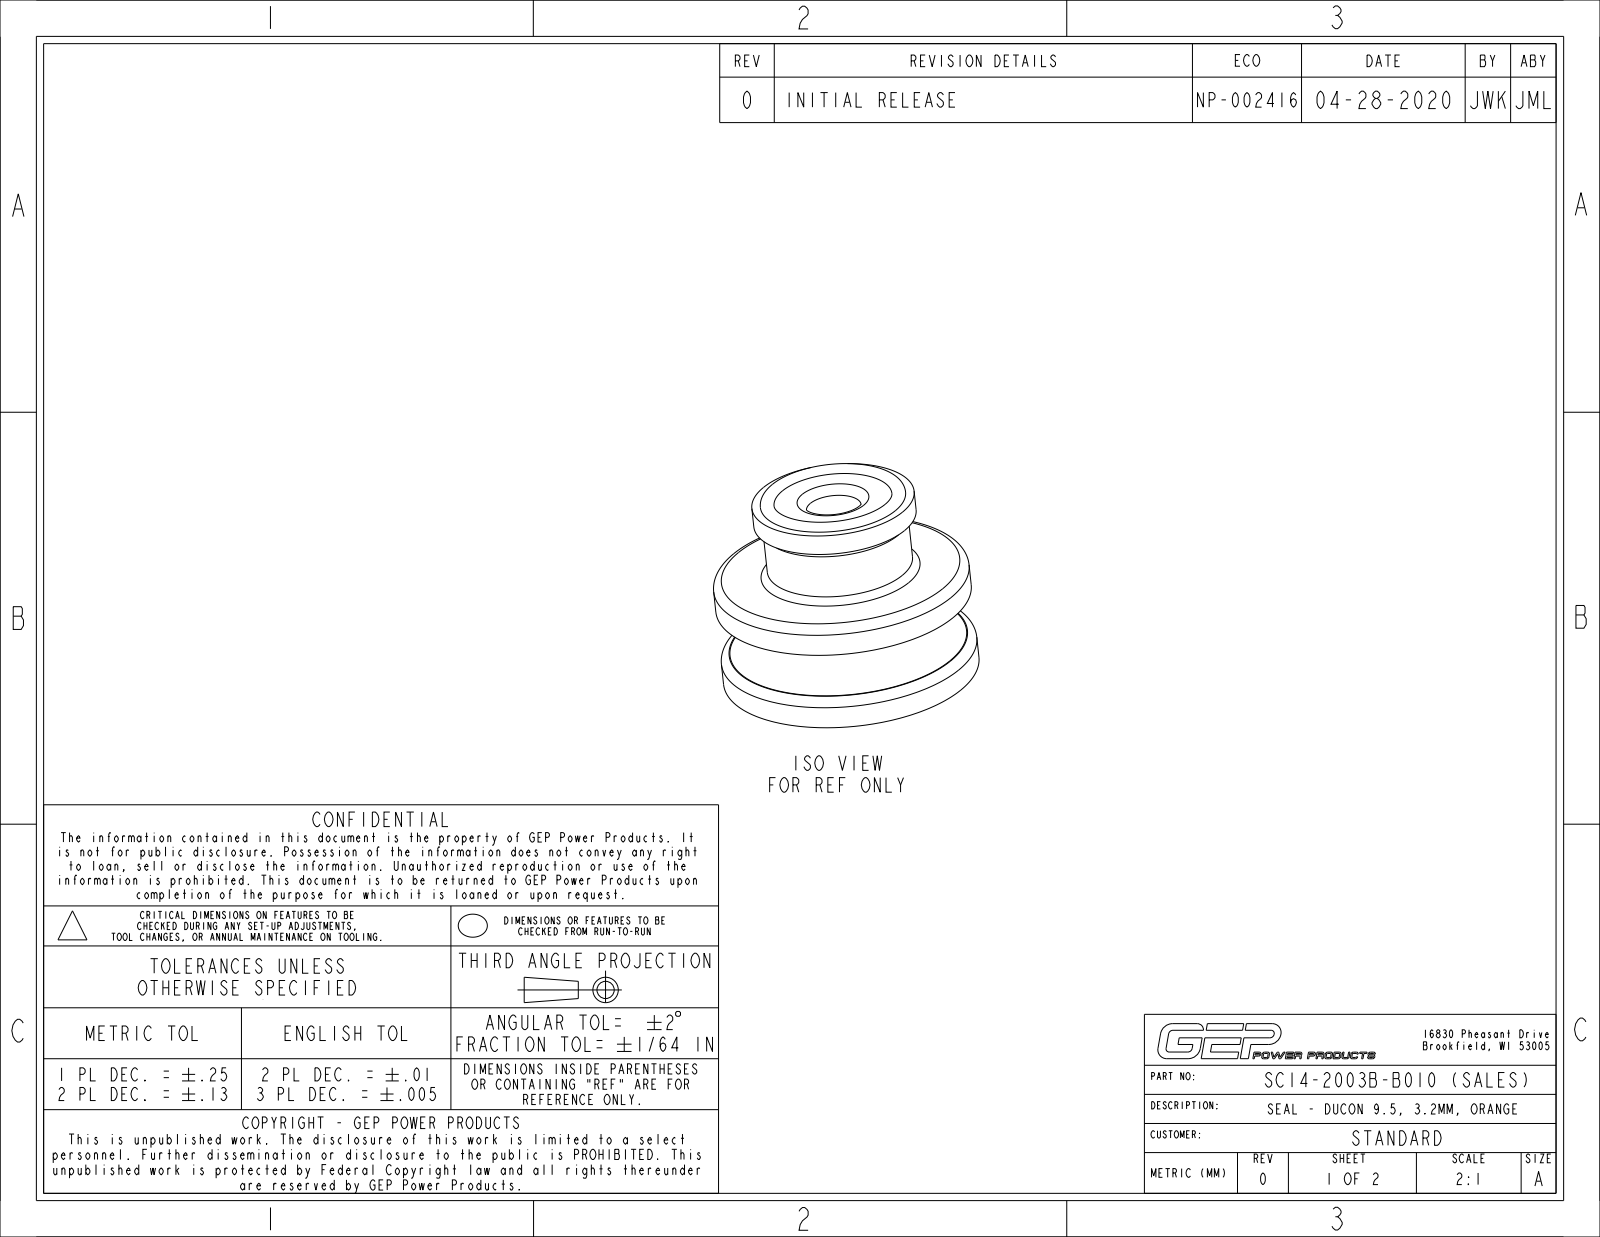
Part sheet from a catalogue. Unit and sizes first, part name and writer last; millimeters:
Units: millimetres
Overall size (bounding box): 14.95 × 14.95 × 12.1
Round holes (diameter × count): ⌀3.2 ×1
Round bosses / shafts (diameter × count): ⌀14.95 ×1, ⌀9.5 ×1, ⌀8.5 ×1
Main face-to-face distances: 6.5, 11.1, 4.6, 1.8, 4.7, 6.4, 9.9, 5.2, 3.4, 1.2
Volume: 1 132 mm³ · Surface area: 1 006 mm²
Bodies: 1 solid, 88 faces (42 planar, 10 cylindrical, 36 other)
Part name (STEP PRODUCT): PC14-2003B-B010_NCF; SC14-2003B-B010_NCF_ASM
STEP written by: CREO PARAMETRIC BY PTC INC, 2017110 (CONFIG_CONTROL_DESIGN)
